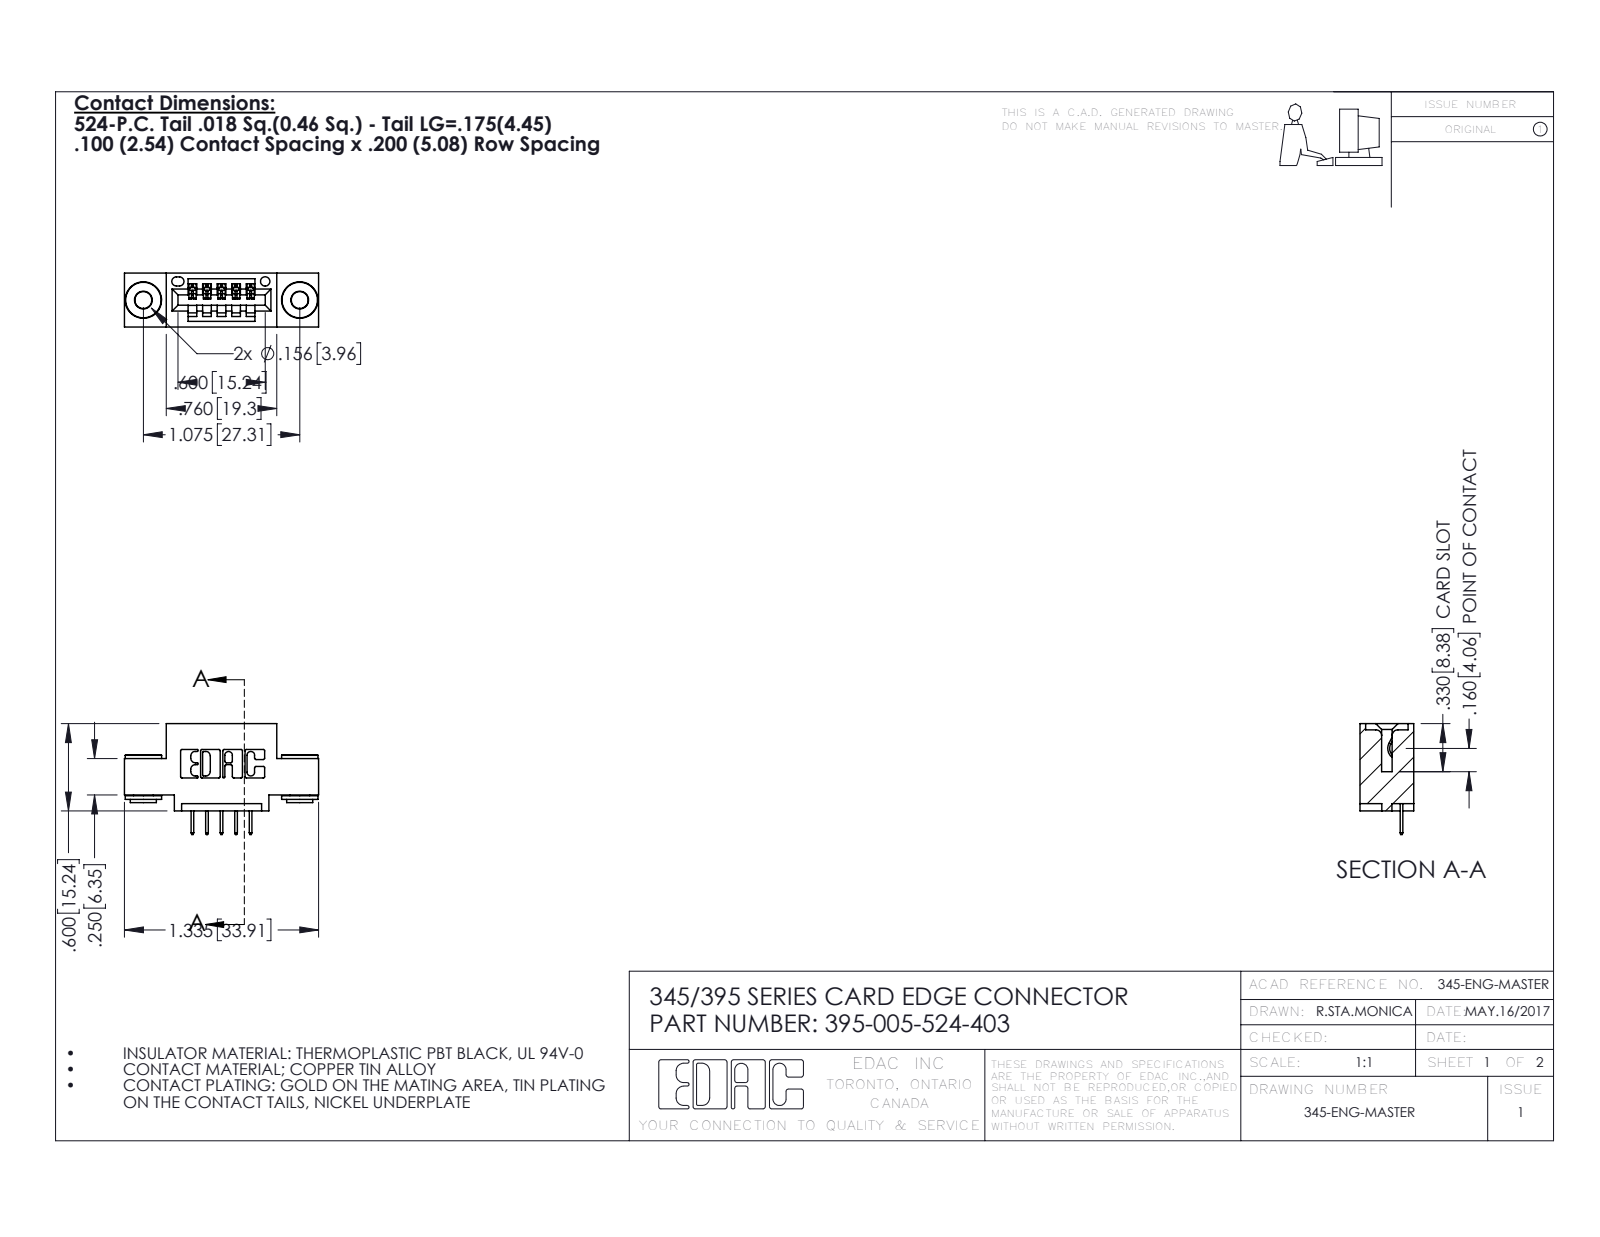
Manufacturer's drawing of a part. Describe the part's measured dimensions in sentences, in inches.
The part is named "345-292-001_345-293-124; 345-250-002_345-250-002-102; 395-005-524-403; 345 Part_0.110 Offset - 0.156 Dia-TH". Its 3-D file was written by "SolidWorks 2016 (CONFIG_CONTROL_DESIGN)". It is 8 solids with 478 faces: 324 planar, 146 cylindrical and 8 other. Overall it measures 1.335 by 0.762 by 0.37 inches. Its volume is 0.174 cubic inches and its surface area 5.44 square inches. Round holes: 2 of diameter 0.116, 2 of diameter 0.156, 1 of diameter 0.064. Round bosses or shafts: 2 of diameter 0.25, 2 of diameter 0.18, 2 of diameter 0.136. Partial cylindrical surfaces (rounded edges, fillets, slot ends): 22 of radius 0.01, 10 of radius 0.006, 6 of radius 0.007, 6 of radius 0.031, 3 of radius 0.026, 2 of radius 0.031, 2 of radius 0.04, 1 of radius 0.014. The main face-to-face distances are 0.37, 0.2, 0.1, 0.072, 0.298, 0.025, 0.25, 0.06, 0.16, 0.55. The hole center spacings are 0.27, 0.847, 1.075.
